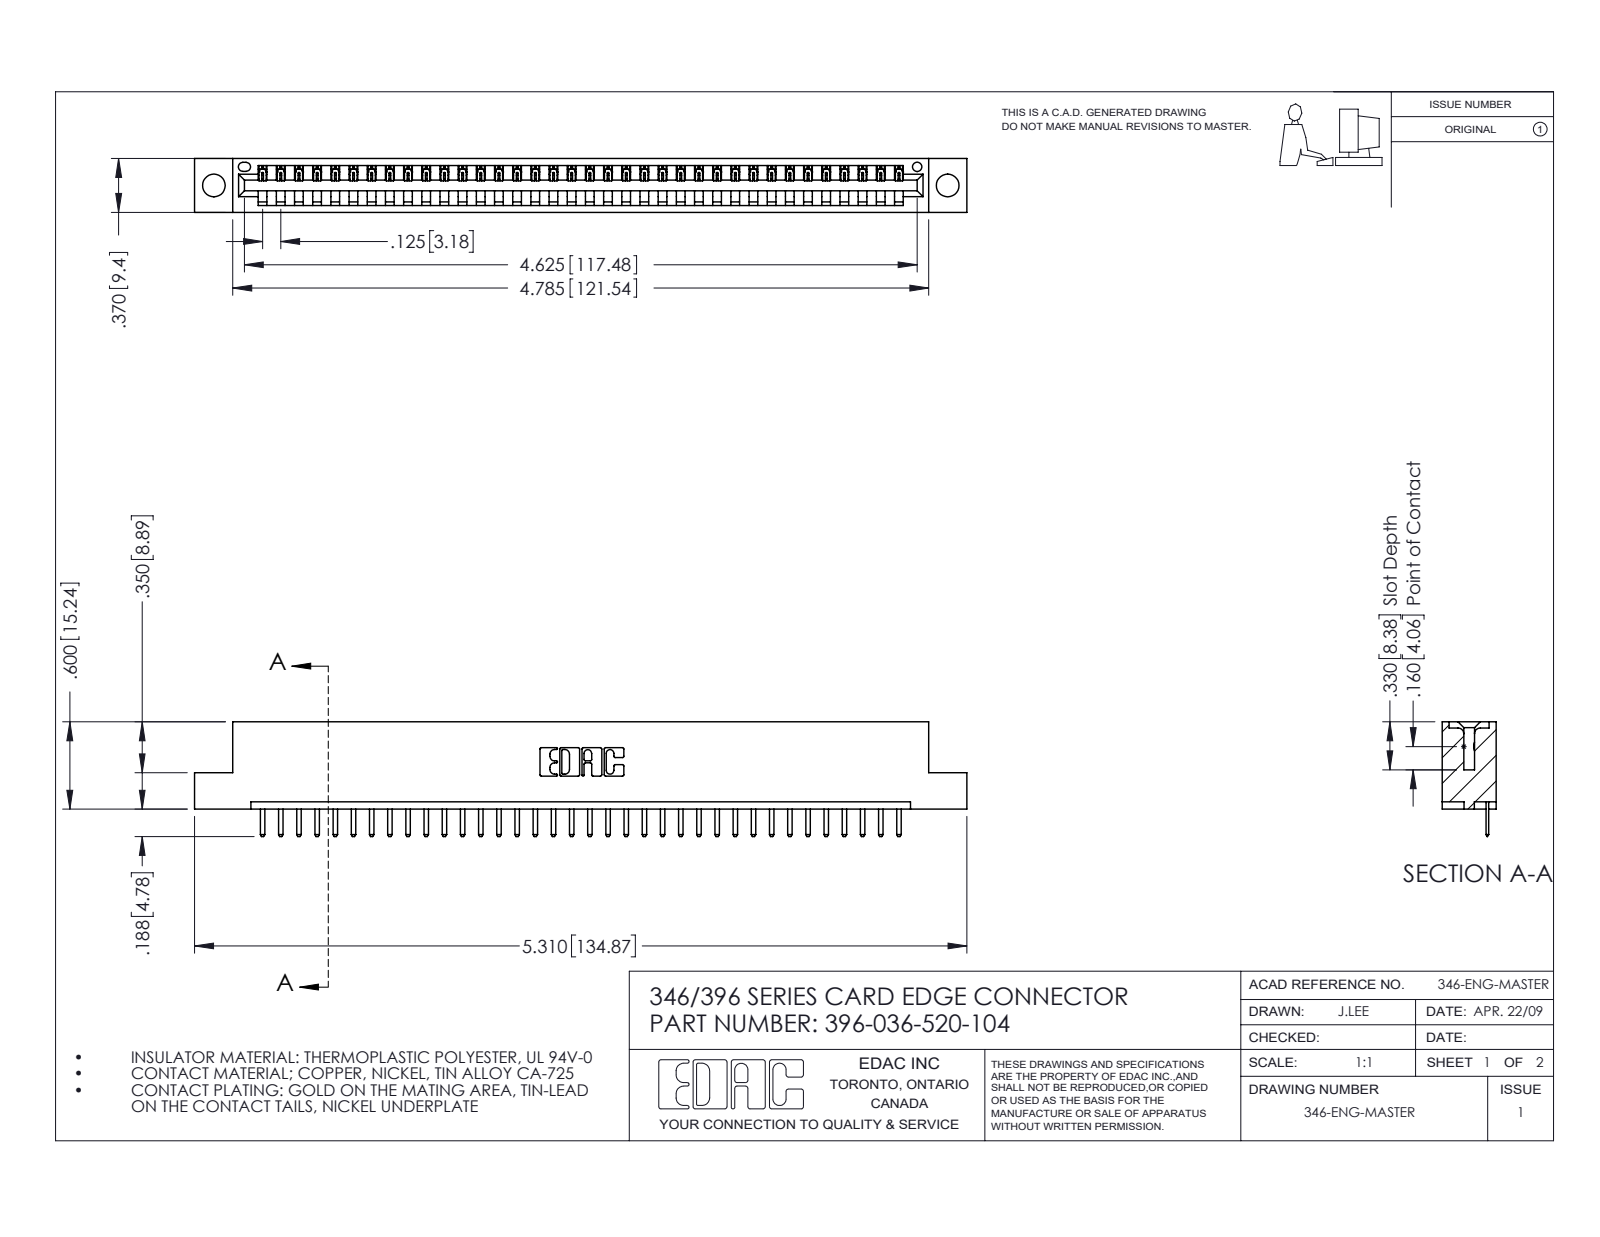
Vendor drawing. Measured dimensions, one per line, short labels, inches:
name: 396-036-520-104; 345-292-001_345-293-120; 346 Part_Flush Mounting Lugs - 0.156 Dia-TH
written by: SolidWorks 2016 (CONFIG_CONTROL_DESIGN)
unit: in
bodies: 37 solids, 2354 faces (1588 planar, 766 cylindrical, 0 other)
size: 5.31 × 0.788 × 0.37
volume: 0.774 in³; area: 23.62 in²
holes: 2× ⌀0.156, 1× ⌀0.064
rounds: 74× R0.01, 72× R0.006, 22× R0.01, 6× R0.007, 6× R0.031, 3× R0.026, 2× R0.031, 2× R0.04
face distances: 0.048, 0.322, 0.37, 0.25, 0.148, 0.222, 0.1, 0.174, 0.072, 0.298
hole spacings: 0.246, 4.836, 5.045
